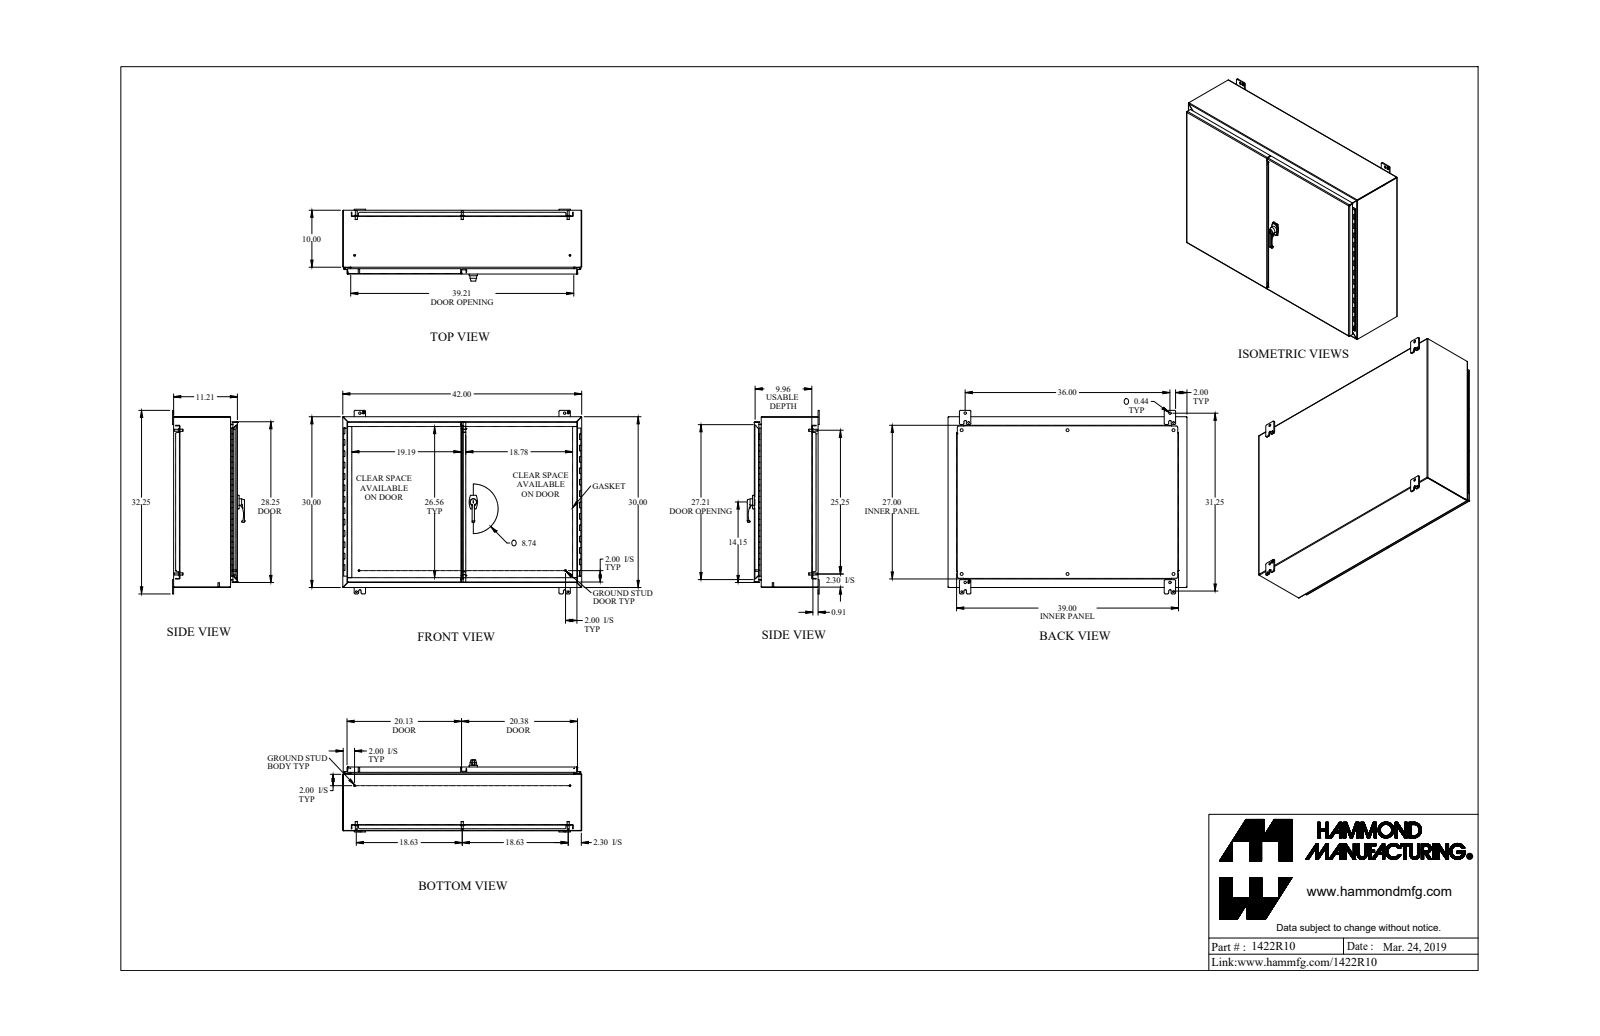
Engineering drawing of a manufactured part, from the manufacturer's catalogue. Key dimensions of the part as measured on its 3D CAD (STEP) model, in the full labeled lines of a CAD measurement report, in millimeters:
Part name (STEP PRODUCT): 1422R10
STEP written by: SolidWorks 2019 (AUTOMOTIVE_DESIGN)
Units: millimetres
Bodies: 0 solids, 1669 faces (1024 planar, 495 cylindrical, 150 other)
Overall size (bounding box): 1066.8 × 819.2 × 321
Round holes (diameter × count): ⌀7.7 ×10, ⌀7.8 ×7, ⌀11.3 ×6, ⌀12.7 ×6, ⌀5.5 ×4, ⌀8 ×4, ⌀11.1 ×4, ⌀5.5 ×3, ⌀2.8 ×2, ⌀3.2 ×2, ⌀4 ×2, ⌀4.7 ×2
Round bosses / shafts (diameter × count): ⌀25.4 ×7, ⌀16.5 ×6, ⌀9.5 ×6, ⌀8.4 ×6, ⌀12.7 ×5, ⌀8 ×4, ⌀7.1 ×4, ⌀6.4 ×4
Partial cylindrical surfaces — rounded edges, fillets, slot ends (radius × count): R4.8 ×36, R1.2 ×18, R3.6 ×18, R0.9 ×16, R1.3 ×16, R2.7 ×16, R6.4 ×13, R2.9 ×12
Main face-to-face distances: 1.8, 280.5, 282.3, 2.4, 2.4, 23.8, 282.9, 284.7, 256.7, 254.3
Hole centre spacings: 473.1, 152.4, 1037.2, 43, 304.8, 513.2, 808.9, 986.2
